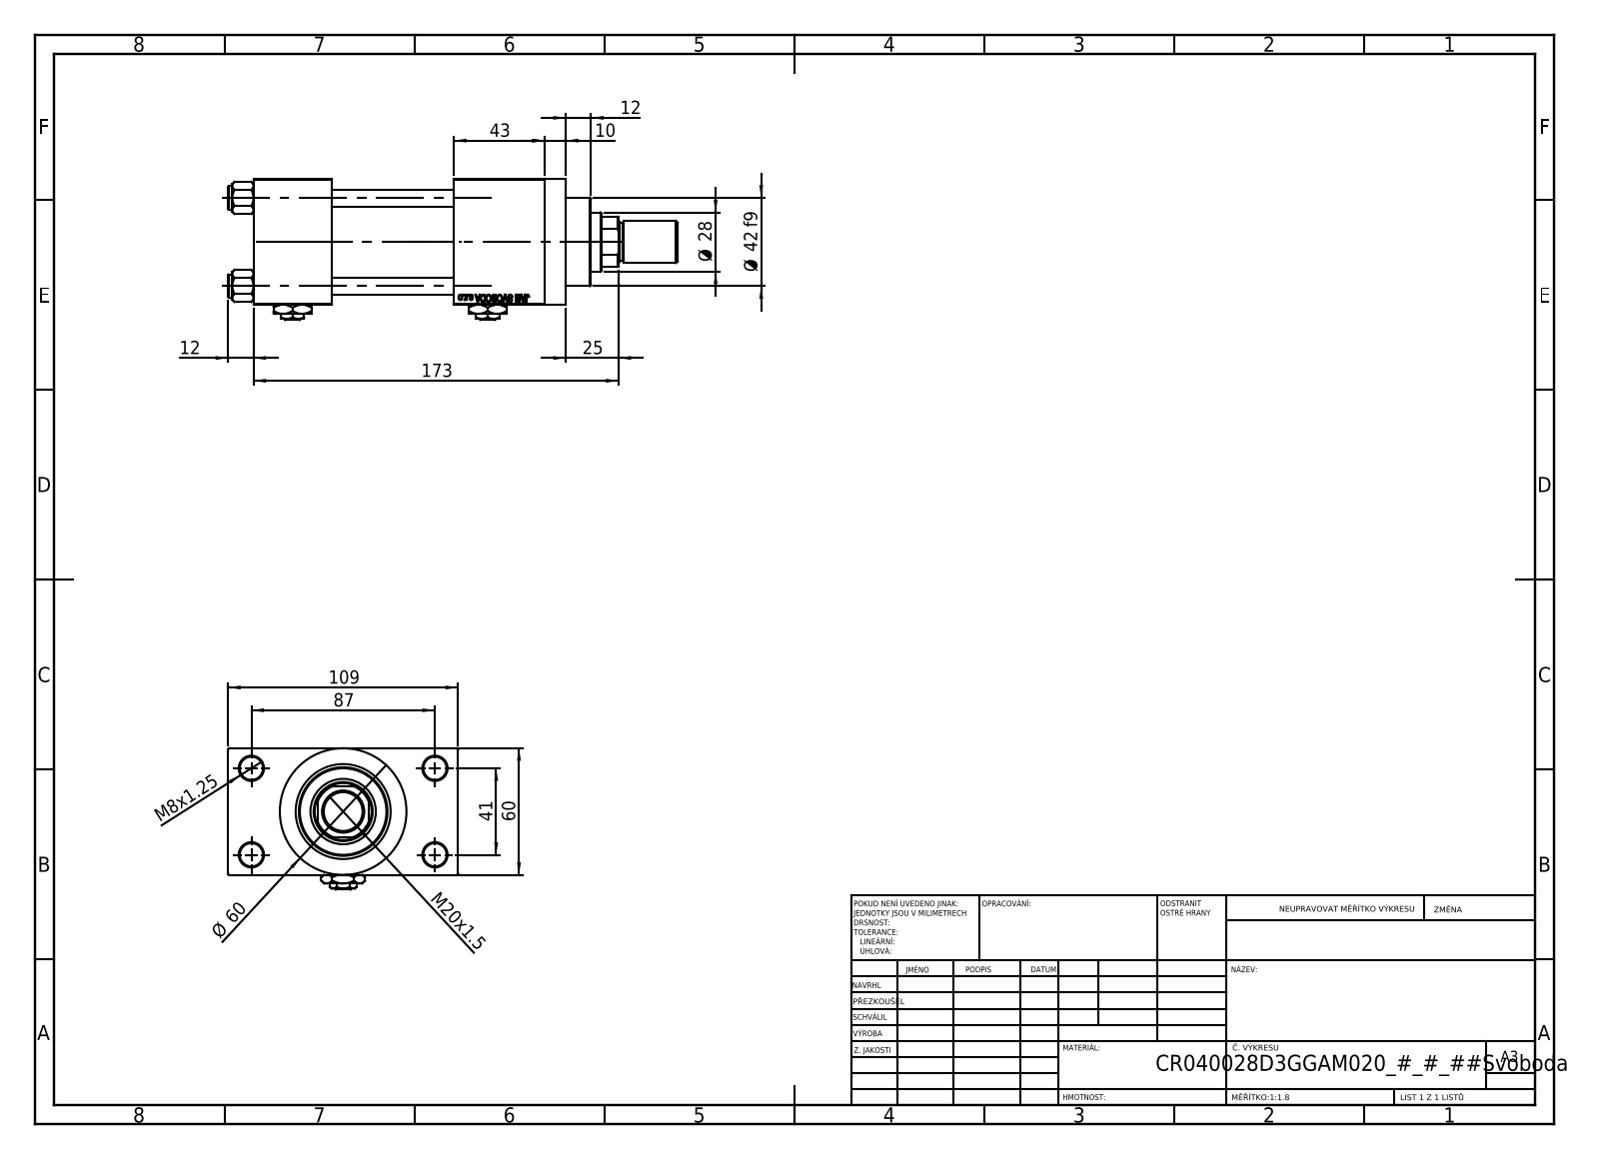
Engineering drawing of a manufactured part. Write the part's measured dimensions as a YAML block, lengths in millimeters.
part_name: "NUT_M5_D; V215CR_VCP_D; V215CR_D_TYCINKA; ROD_END_AH (+3 more)"
step_written_by: "SolidWorks 2019 (CONFIG_CONTROL_DESIGN)"
units: millimeters
bodies: {solids: 14, faces: 1220, planar: 550, cylindrical: 104, other: 566}
overall_size: [213, 109, 67]
volume: 540599
surface_area: 132908
round_holes:
  - {diameter: 8, count: 4}
  - {diameter: 11, count: 4}
  - {diameter: 7, count: 2}
  - {diameter: 16.66, count: 2}
  - {diameter: 24, count: 2}
  - {diameter: 18.5, count: 1}
  - {diameter: 28, count: 1}
  - {diameter: 31, count: 1}
  - {diameter: 40, count: 1}
  - {diameter: 45, count: 1}
round_bosses_or_shafts:
  - {diameter: 11, count: 4}
  - {diameter: 60, count: 1}
  - {diameter: 46, count: 1}
  - {diameter: 42, count: 1}
  - {diameter: 20, count: 1}
  - {diameter: 18, count: 1}
partial_cylinders:
  - {radius: 13.5, count: 1}
face_to_face_distances: [60, 84.5, 24.5, 58, 37, 95, 138, 101, 43, 109]
hole_center_spacings: [22.65, 29.49, 41.7, 47.15, 48.09, 64.35, 76.49, 41]
